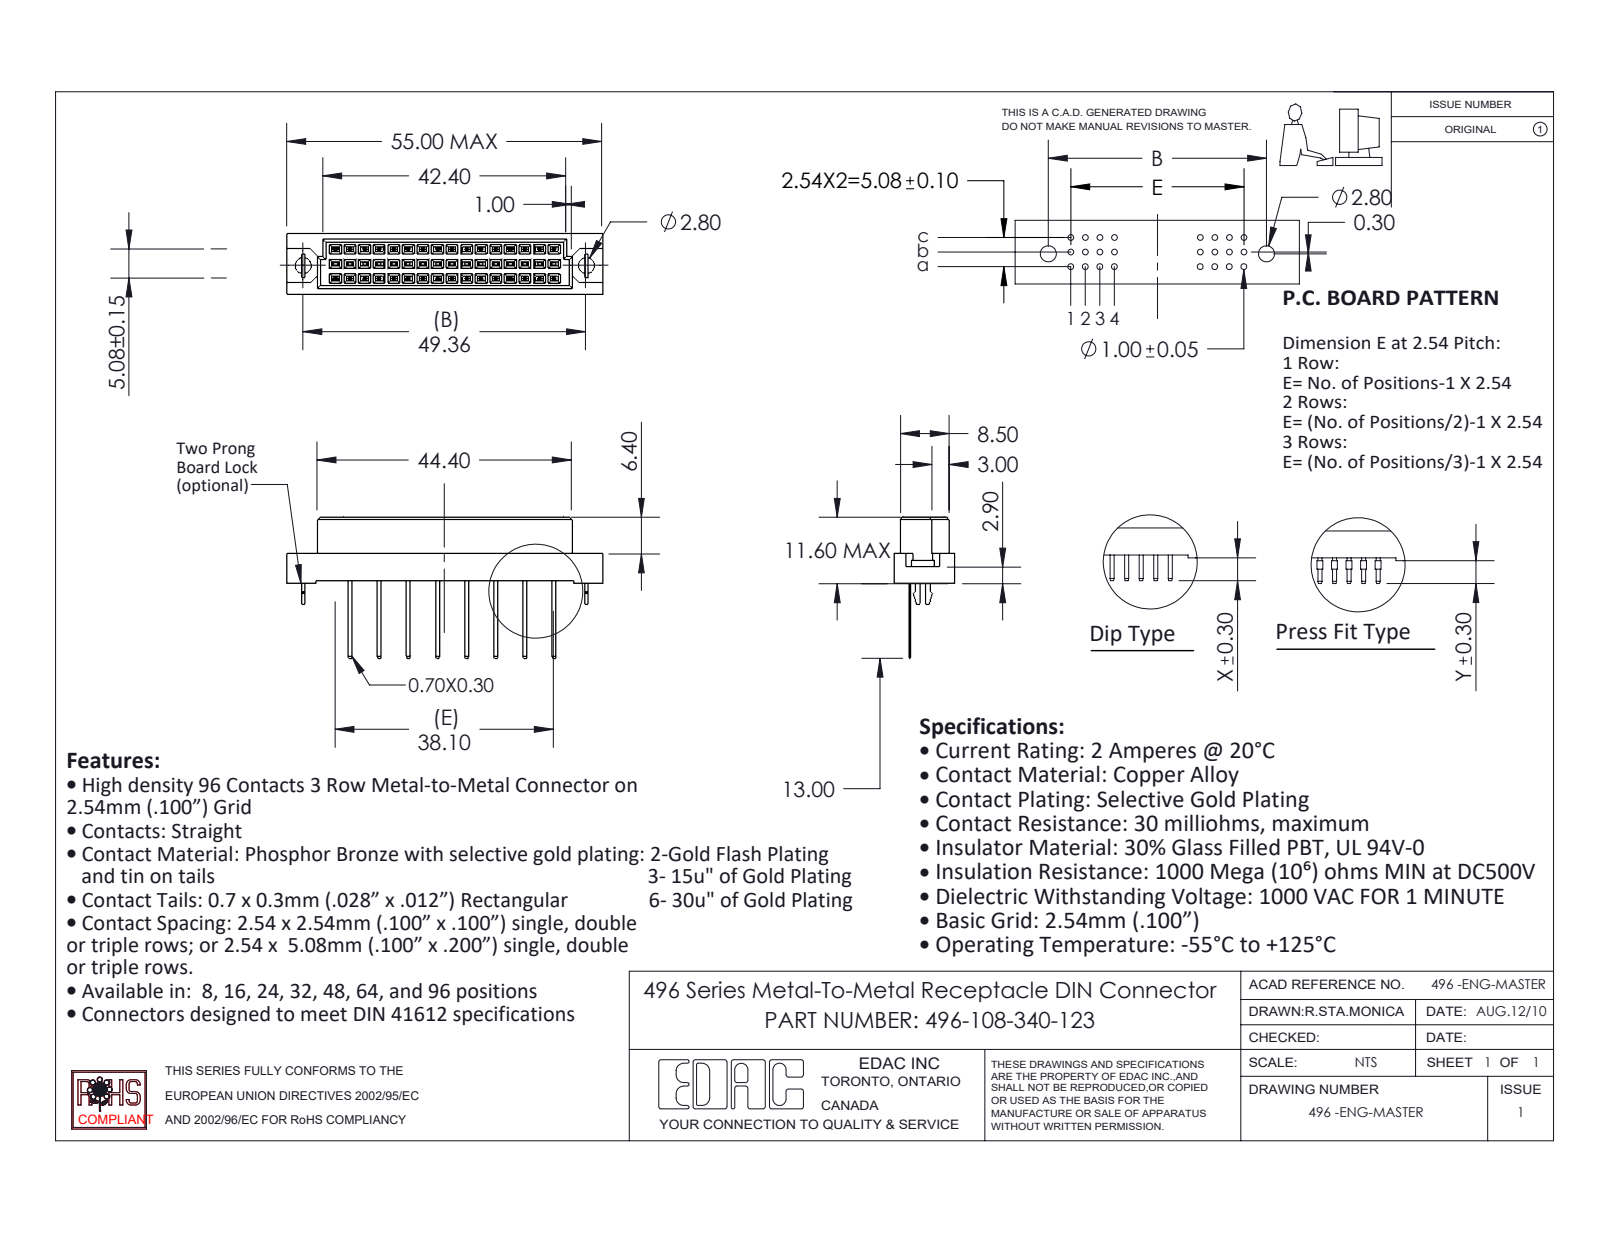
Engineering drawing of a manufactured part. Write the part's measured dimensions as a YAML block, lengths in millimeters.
part_name: "496 Part_48; 496-108-340-123; 496 Bore-lock; 496-290_40"
step_written_by: "SolidWorks 2020 (CONFIG_CONTROL_DESIGN)"
units: millimeters
bodies: {solids: 11, faces: 782, planar: 776, cylindrical: 6, other: 0}
overall_size: [55, 24.6, 10.6]
volume: 4642
surface_area: 4615
round_holes:
  - {diameter: 2.8, count: 2}
partial_cylinders:
  - {radius: 0.53, count: 1}
face_to_face_distances: [2.54, 1.05, 9.55, 5.08, 0.81, 10.6, 3.35, 1.73, 8.5, 0.56]
hole_center_spacings: [49.36]
